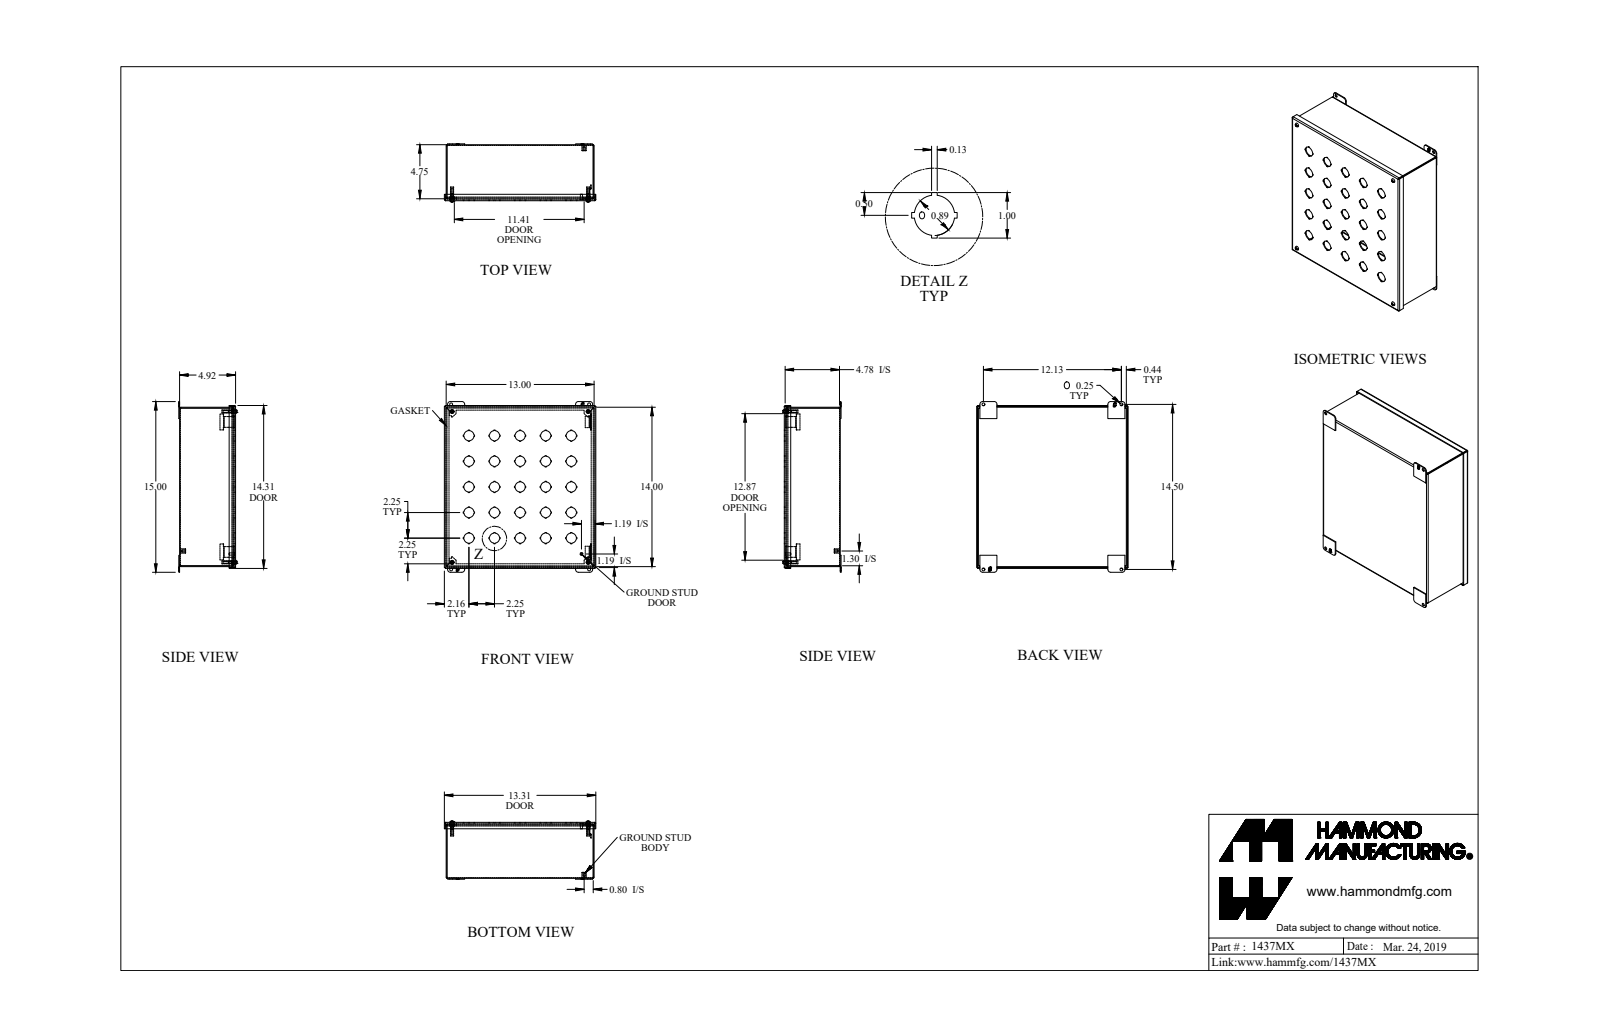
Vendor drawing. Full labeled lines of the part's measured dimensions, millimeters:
Part name (STEP PRODUCT): 1437MX_Default
STEP written by: SolidWorks 2019 (CONFIG_CONTROL_DESIGN)
Units: millimetres
Bodies: 23 solids, 1115 faces (799 planar, 260 cylindrical, 56 other)
Overall size (bounding box): 381 × 338.1 × 130.1
Volume: 855 600 mm³ · Surface area: 903 900 mm²
Round holes (diameter × count): ⌀22.5 ×25, ⌀6.4 ×8, ⌀4 ×4, ⌀10.3 ×4, ⌀4 ×1
Round bosses / shafts (diameter × count): ⌀9.9 ×4, ⌀7 ×4, ⌀4.8 ×4, ⌀3.8 ×4, ⌀9.5 ×1, ⌀6.4 ×1, ⌀4.8 ×1
Partial cylindrical surfaces — rounded edges, fillets, slot ends (radius × count): R0.9 ×12, R2.7 ×12, R6.4 ×8, R0.7 ×4, R2.2 ×4, R4.1 ×4, R4.3 ×4, R3.2 ×2
Main face-to-face distances: 1.8, 123.2, 125, 121.4, 328.4, 353.8, 330.2, 326.5, 355.6, 351.9
Hole centre spacings: 57.2, 127.8, 80.8, 114.3, 180.7, 16, 161.6, 171.5
